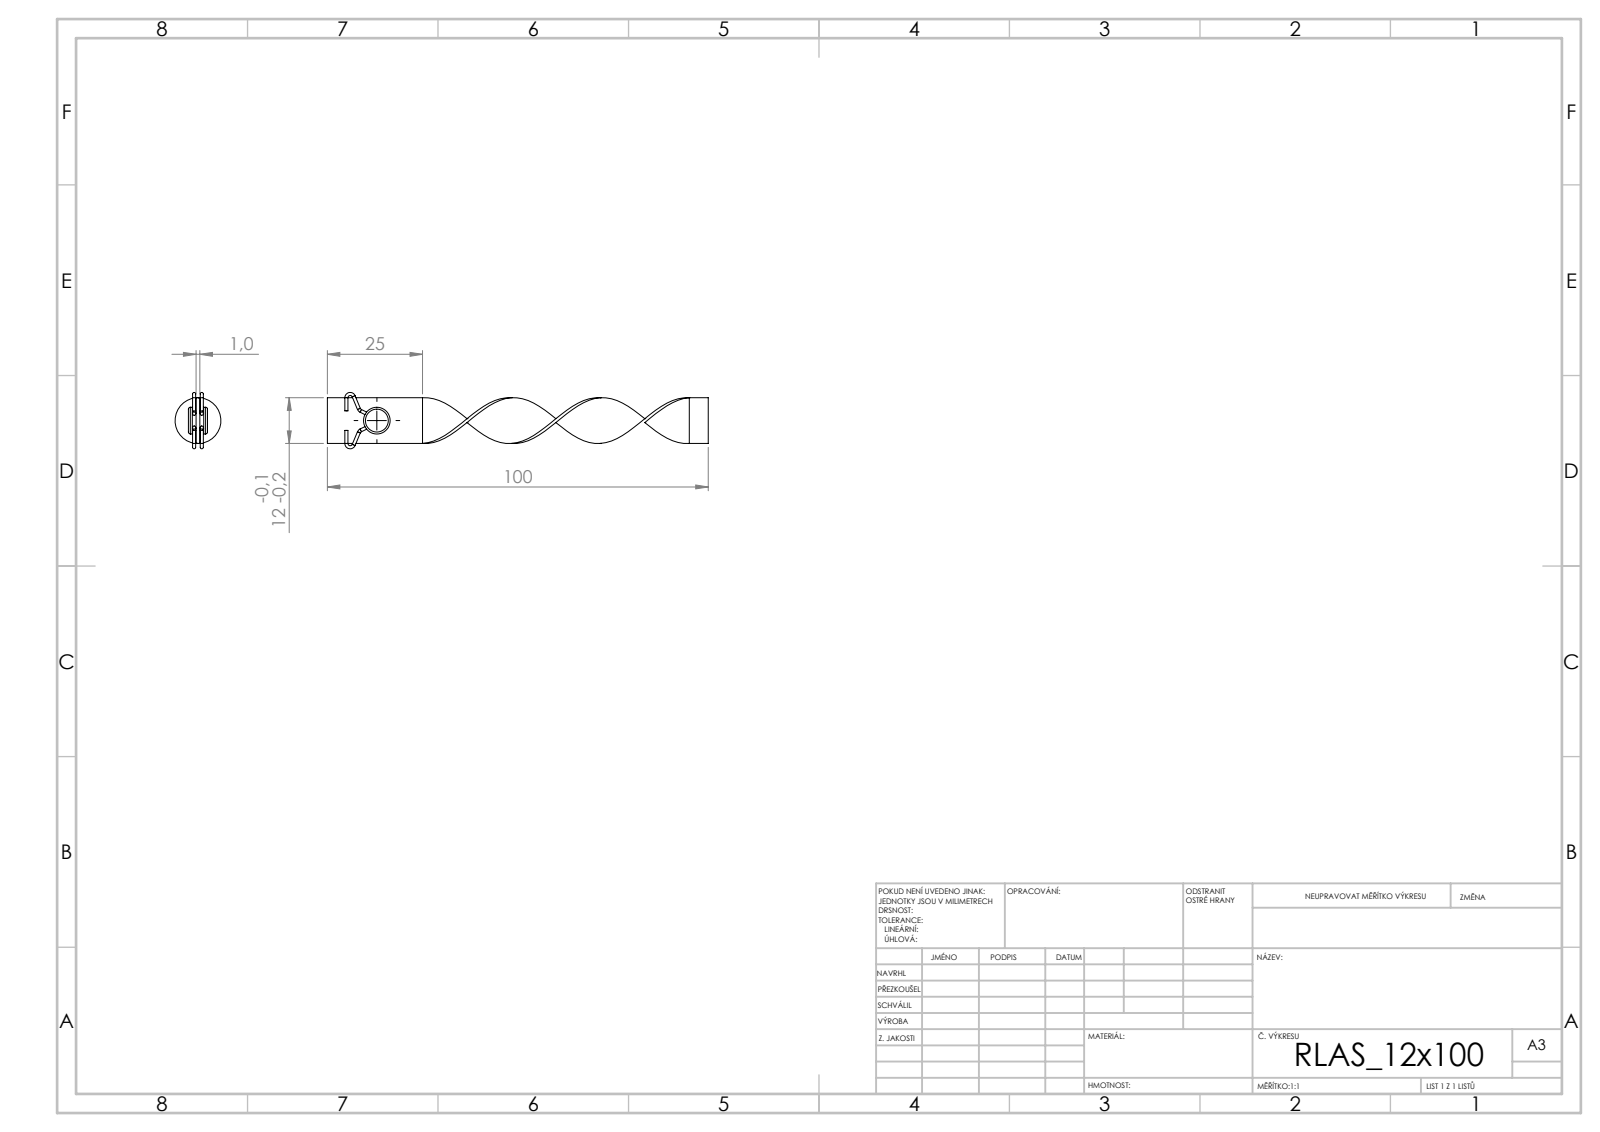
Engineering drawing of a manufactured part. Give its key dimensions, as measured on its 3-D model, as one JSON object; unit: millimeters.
{"step_written_by": "SolidWorks 2019 (CONFIG_CONTROL_DESIGN)", "units": "millimeters", "bodies": {"solids": 3, "faces": 90, "planar": 18, "cylindrical": 40, "other": 32}, "overall_size": [100, 14.8, 12.04], "volume_mm3": 1338, "surface_area_mm2": 3150, "round_bosses_or_shafts": [[0.8, 14], [7, 1], [4, 1]], "face_to_face_distances": [1, 2, 3, 4, 12, 5, 100, 3.45, 8.55, 5.1]}
